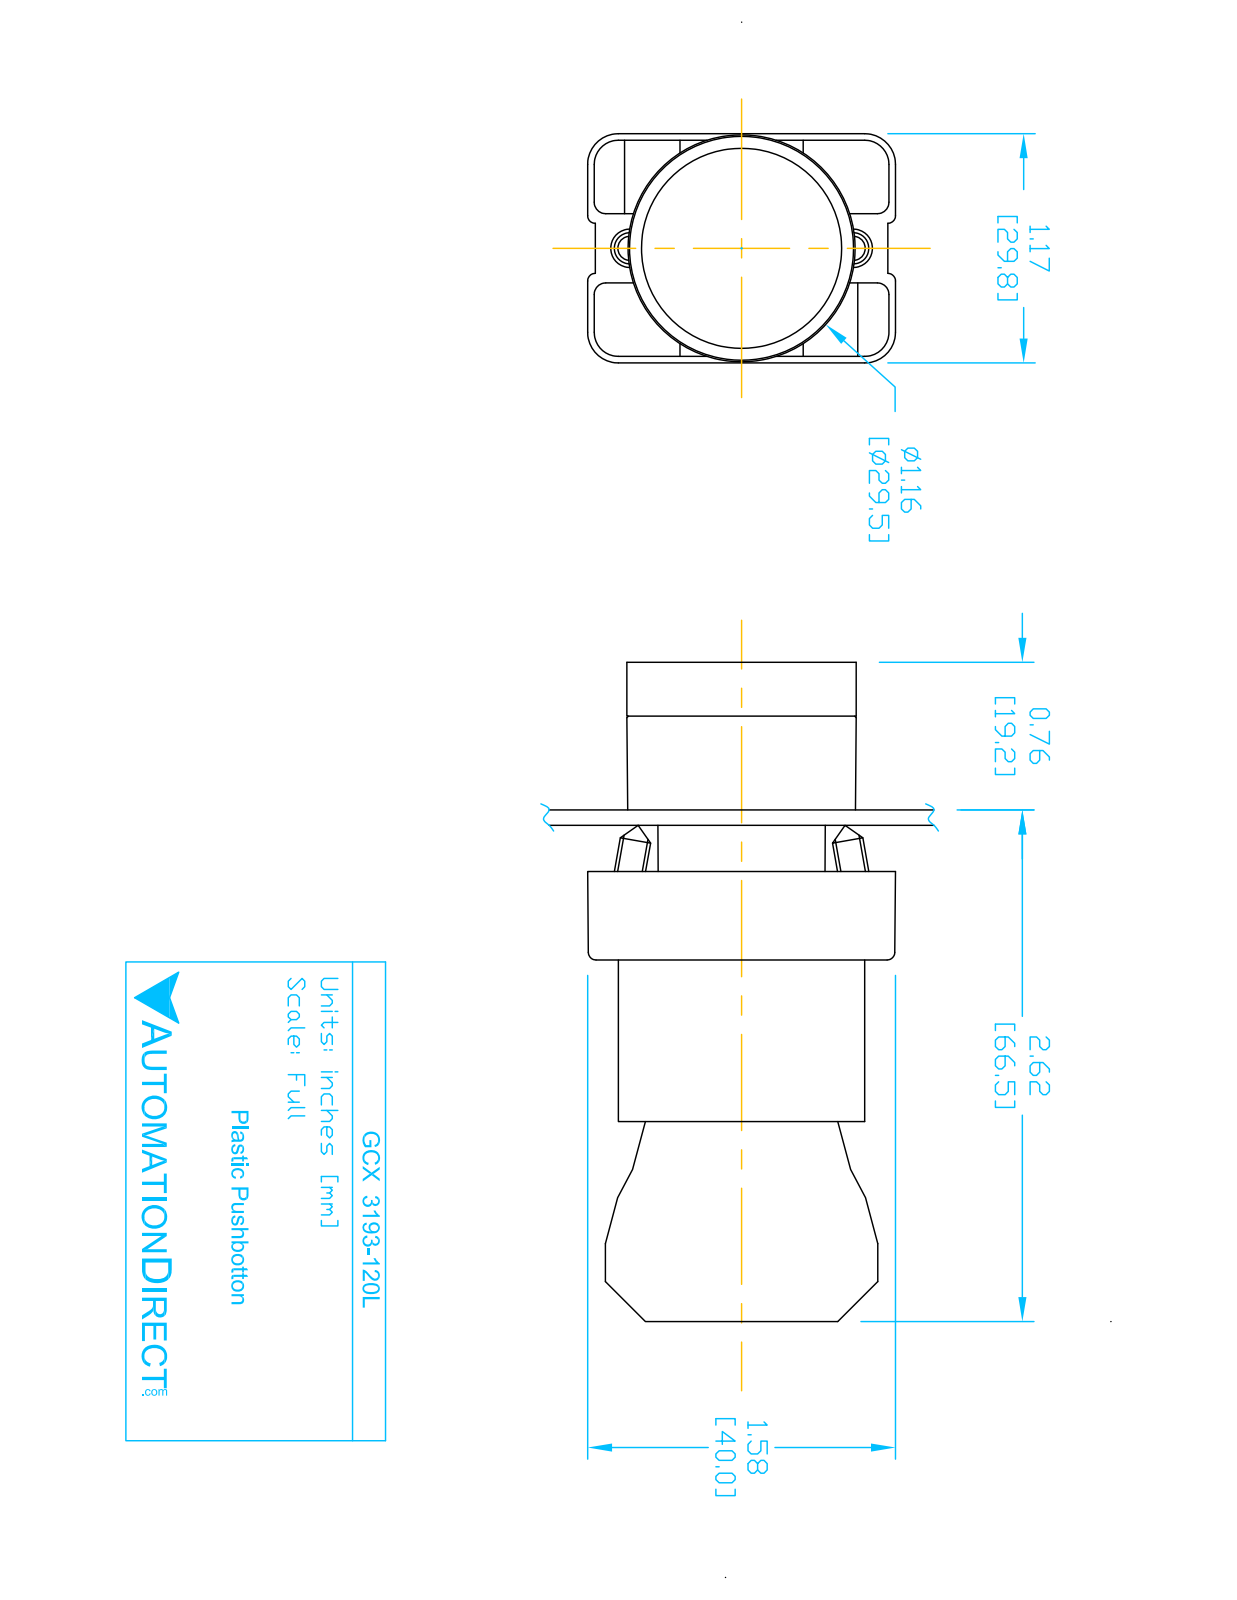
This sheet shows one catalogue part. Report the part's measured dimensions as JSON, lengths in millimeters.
{"part_name": "GCX3193-120L; ECX1050; ECX3029-2; CONTACT BLOCK (+1 more)", "step_written_by": "SolidWorks 2016 (AUTOMOTIVE_DESIGN)", "units": "millimeters", "bodies": {"solids": 8, "faces": 431, "planar": 252, "cylindrical": 148, "other": 31}, "overall_size": [84.3, 40.2, 29.9], "volume_mm3": 45790, "surface_area_mm2": 25010, "round_holes": [[2, 2], [3.1, 2], [3.3, 2], [2.2, 1], [5, 1], [11.9, 1], [22.3, 1], [22.6, 1], [26, 1]], "round_bosses_or_shafts": [[4, 4], [29.8, 1], [25.5, 1], [24, 1], [21.7, 1], [19.8, 1], [12.8, 1]], "partial_cylinders_radius": [[1.5, 24], [1, 12], [3.1, 12], [4, 12], [1, 8], [3.3, 2], [0.5, 1], [1.6, 1]], "face_to_face_distances": [21, 14.7, 51.3, 30.3, 29.7, 7, 58.3, 37.3, 0.8, 0.8], "hole_center_spacings": [6, 13.8, 12, 12.4]}
